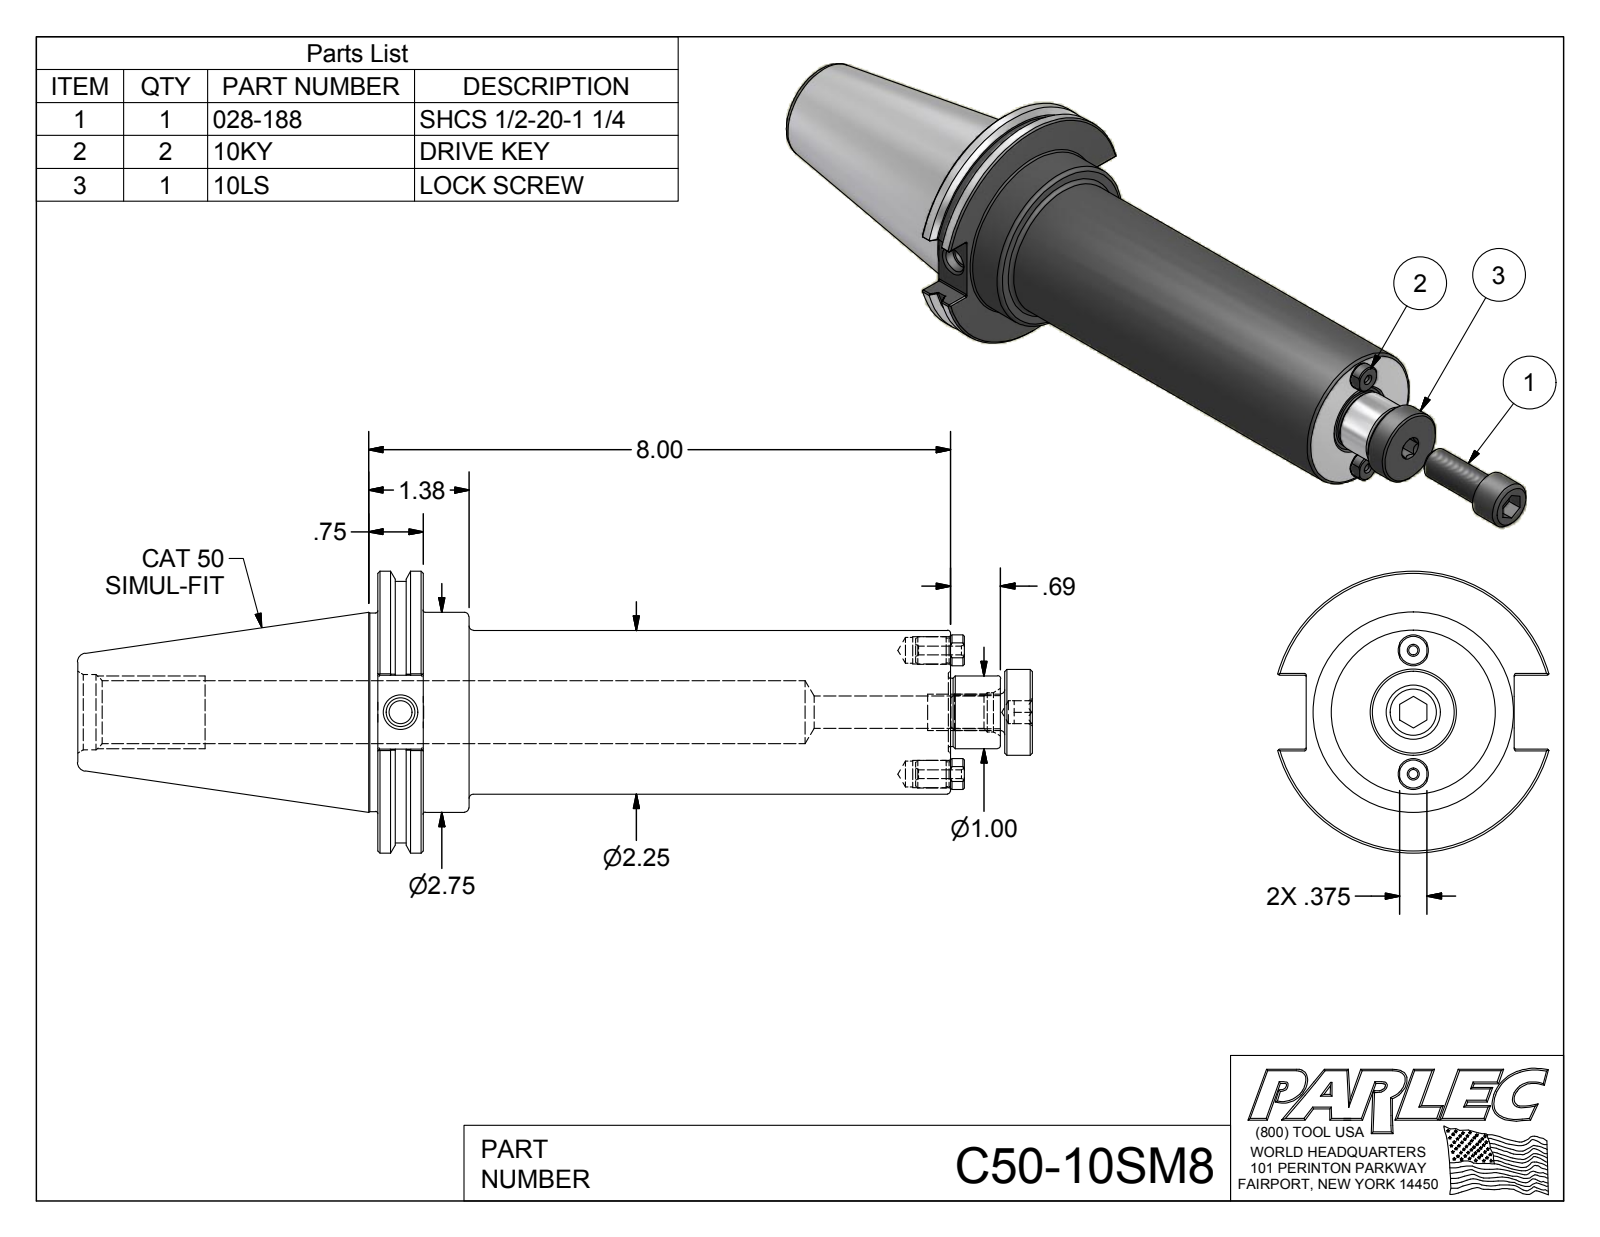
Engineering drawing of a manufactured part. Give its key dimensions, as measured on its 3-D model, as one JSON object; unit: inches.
{"part_name": "C50-10SM8; C50-10SM8-1; 028-188; 10KY (+1 more)", "step_written_by": "Autodesk Inventor 2012 (AUTOMOTIVE_DESIGN)", "units": "inches", "bodies": {"solids": 5, "faces": 177, "planar": 68, "cylindrical": 48, "other": 61}, "overall_size": [15.378, 3.875, 3.729], "volume_in3": 47.36, "surface_area_in2": 153.8, "round_holes": [[0.12, 2], [0.354, 2], [0.374, 2], [0.312, 1], [0.315, 1], [0.399, 1], [0.446, 1], [0.54, 1], [0.865, 1], [1.038, 1]], "round_bosses_or_shafts": [[0.38, 2], [0.34, 2], [3.875, 1], [3.594, 1], [2.75, 1], [2.73, 1], [2.25, 1], [1.18, 1]], "partial_cylinders_radius": [[0.02, 12], [0.214, 2]], "face_to_face_distances": [0.625, 7.875, 7.25, 1.255, 0.63, 6.62, 9.002, 8.377, 7.747, 1.127], "hole_center_spacings": [0.85, 1.7]}
